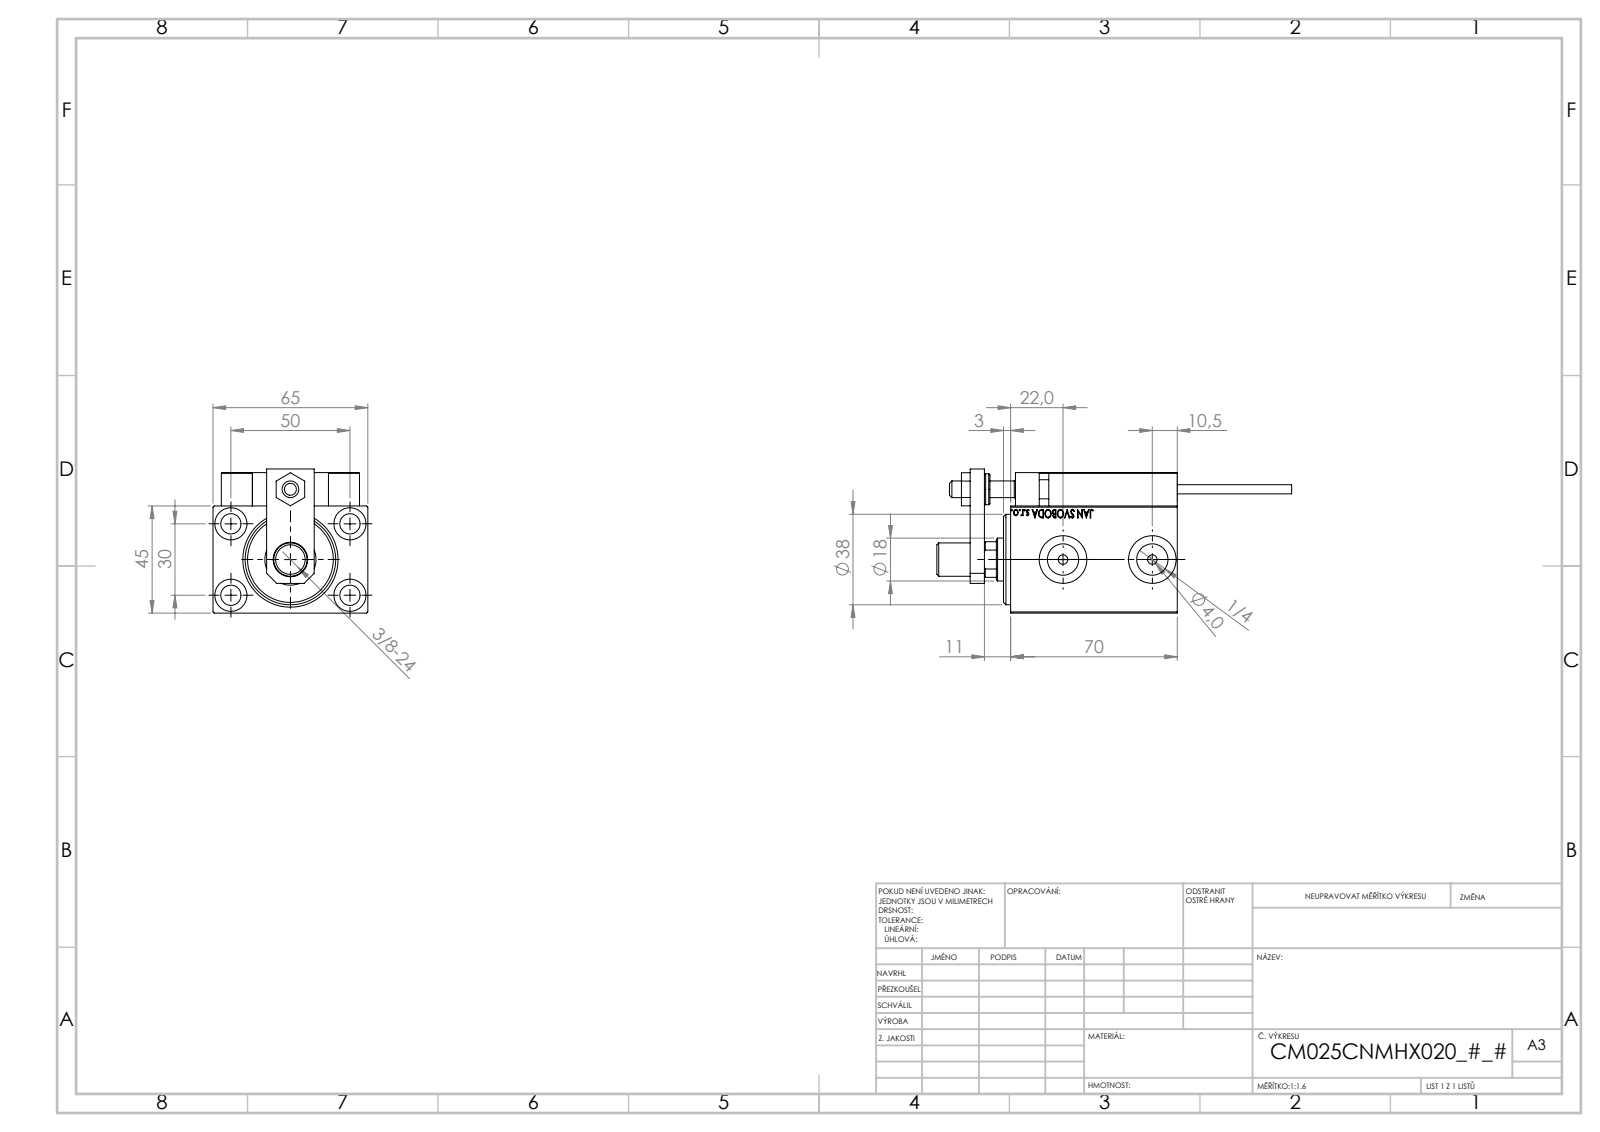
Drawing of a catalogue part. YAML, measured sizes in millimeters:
part_name: "SWITCH_X_FRONT_BACK; SWITCH X; ALLEN BOLT D5; SWITCH DIM B,W (+7 more)"
step_written_by: "SolidWorks 2019 (CONFIG_CONTROL_DESIGN)"
units: millimeters
bodies: {solids: 24, faces: 1295, planar: 563, cylindrical: 192, other: 540}
overall_size: [149, 65, 60.5]
volume: 226016
surface_area: 70376
round_holes:
  - {diameter: 4, count: 6}
  - {diameter: 8, count: 5}
  - {diameter: 8.5, count: 5}
  - {diameter: 3.2, count: 4}
  - {diameter: 13.5, count: 4}
  - {diameter: 5, count: 2}
  - {diameter: 13.16, count: 2}
  - {diameter: 20, count: 2}
  - {diameter: 7, count: 1}
  - {diameter: 14.5, count: 1}
  - {diameter: 18, count: 1}
  - {diameter: 21.5, count: 1}
round_bosses_or_shafts:
  - {diameter: 5, count: 2}
  - {diameter: 3.8, count: 2}
  - {diameter: 14, count: 1}
  - {diameter: 13, count: 1}
  - {diameter: 12, count: 1}
  - {diameter: 11, count: 1}
partial_cylinders:
  - {radius: 0.3, count: 30}
  - {radius: 3, count: 2}
  - {radius: 8.5, count: 1}
face_to_face_distances: [45, 59, 14, 65, 6, 3, 19, 5, 7, 20]
hole_center_spacings: [29.15, 11.37, 20, 22.09, 28.9, 29.59, 29.69, 30]
